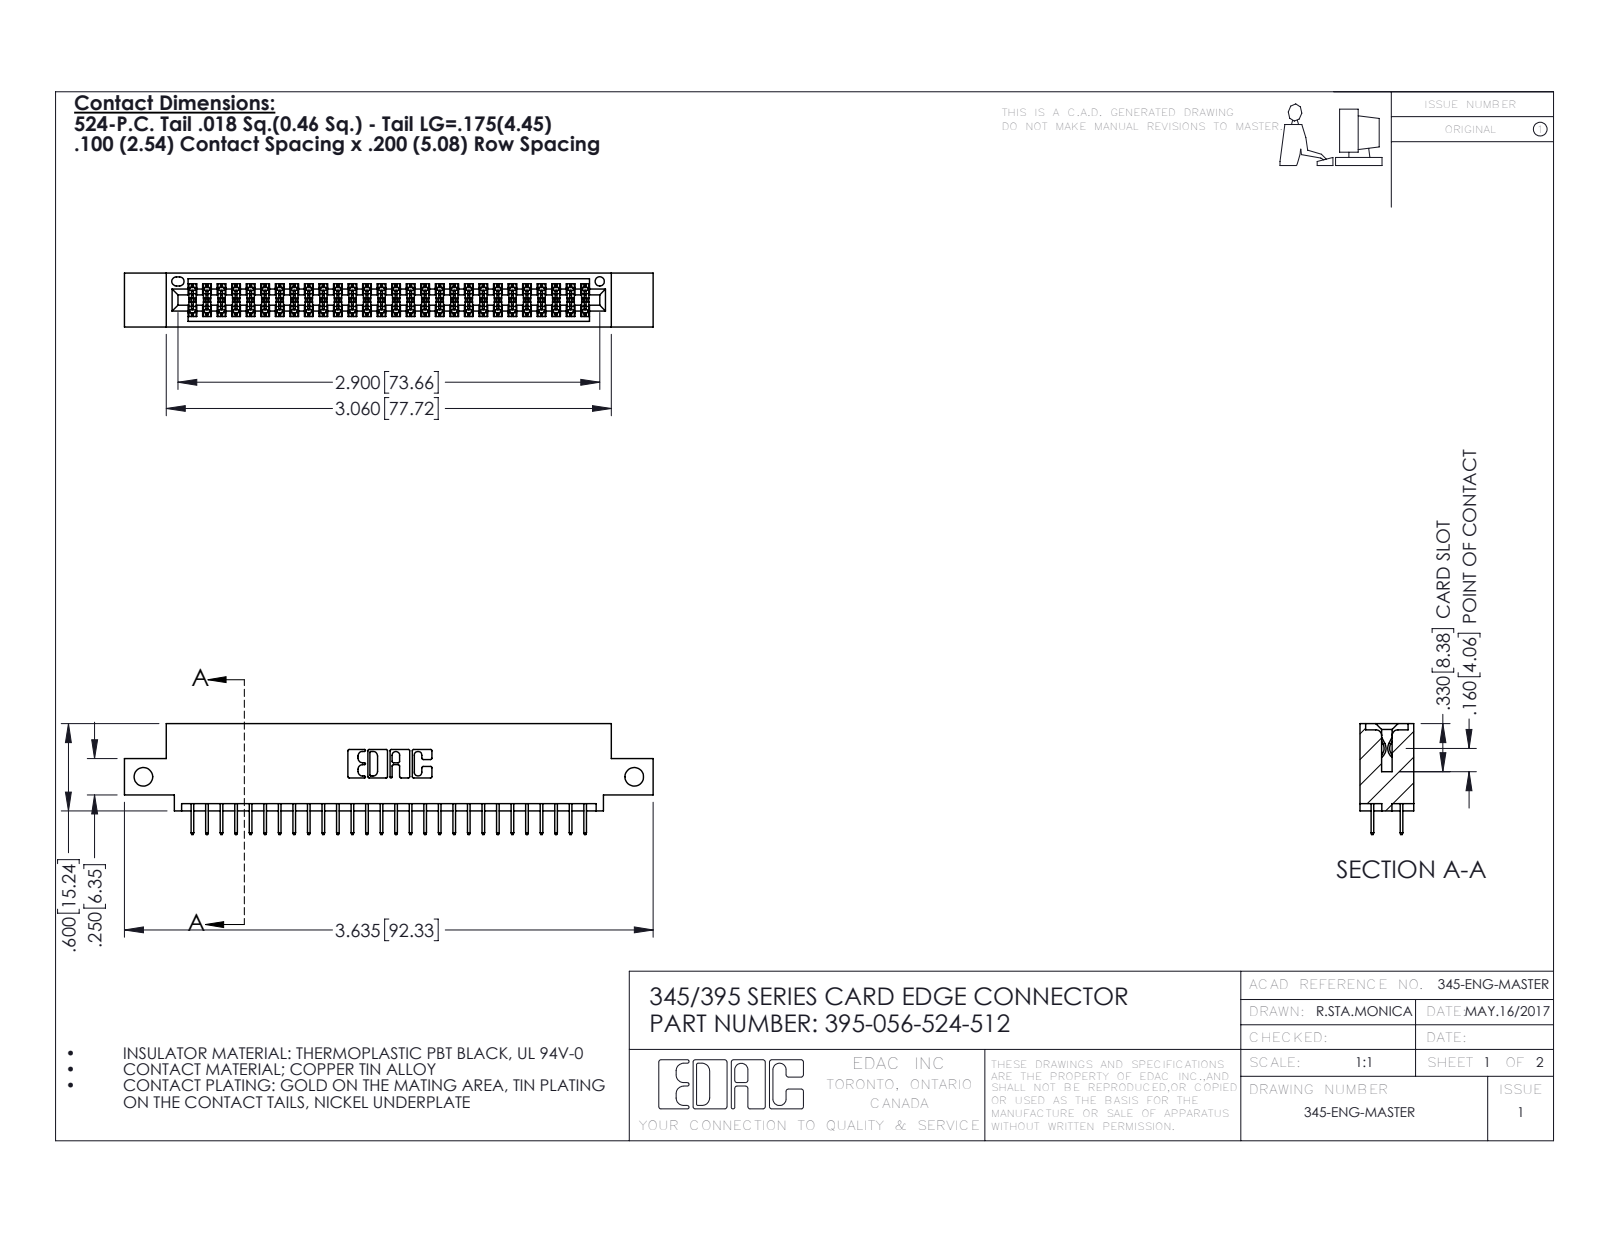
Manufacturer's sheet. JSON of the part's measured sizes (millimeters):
{"part_name": "345 Part_0.110 Offset - Side Mount; 345-292-001_345-293-124; 395-056-524-512", "step_written_by": "SolidWorks 2016 (CONFIG_CONTROL_DESIGN)", "units": "millimeters", "bodies": {"solids": 57, "faces": 3154, "planar": 2268, "cylindrical": 886, "other": 0}, "overall_size": [92.3, 19.4, 9.4], "volume_mm3": 8590, "surface_area_mm2": 12170, "round_holes": [[3.3, 2], [1.6, 1]], "partial_cylinders_radius": [[0.2, 84], [0.3, 22], [0.2, 6], [0.8, 6], [0.7, 3], [0.4, 2], [0.5, 2], [0.6, 2]], "face_to_face_distances": [1.8, 7.6, 5.1, 9.4, 2.5, 6.9, 0.6, 5.7, 1.8, 4.4], "hole_center_spacings": [85.7]}
